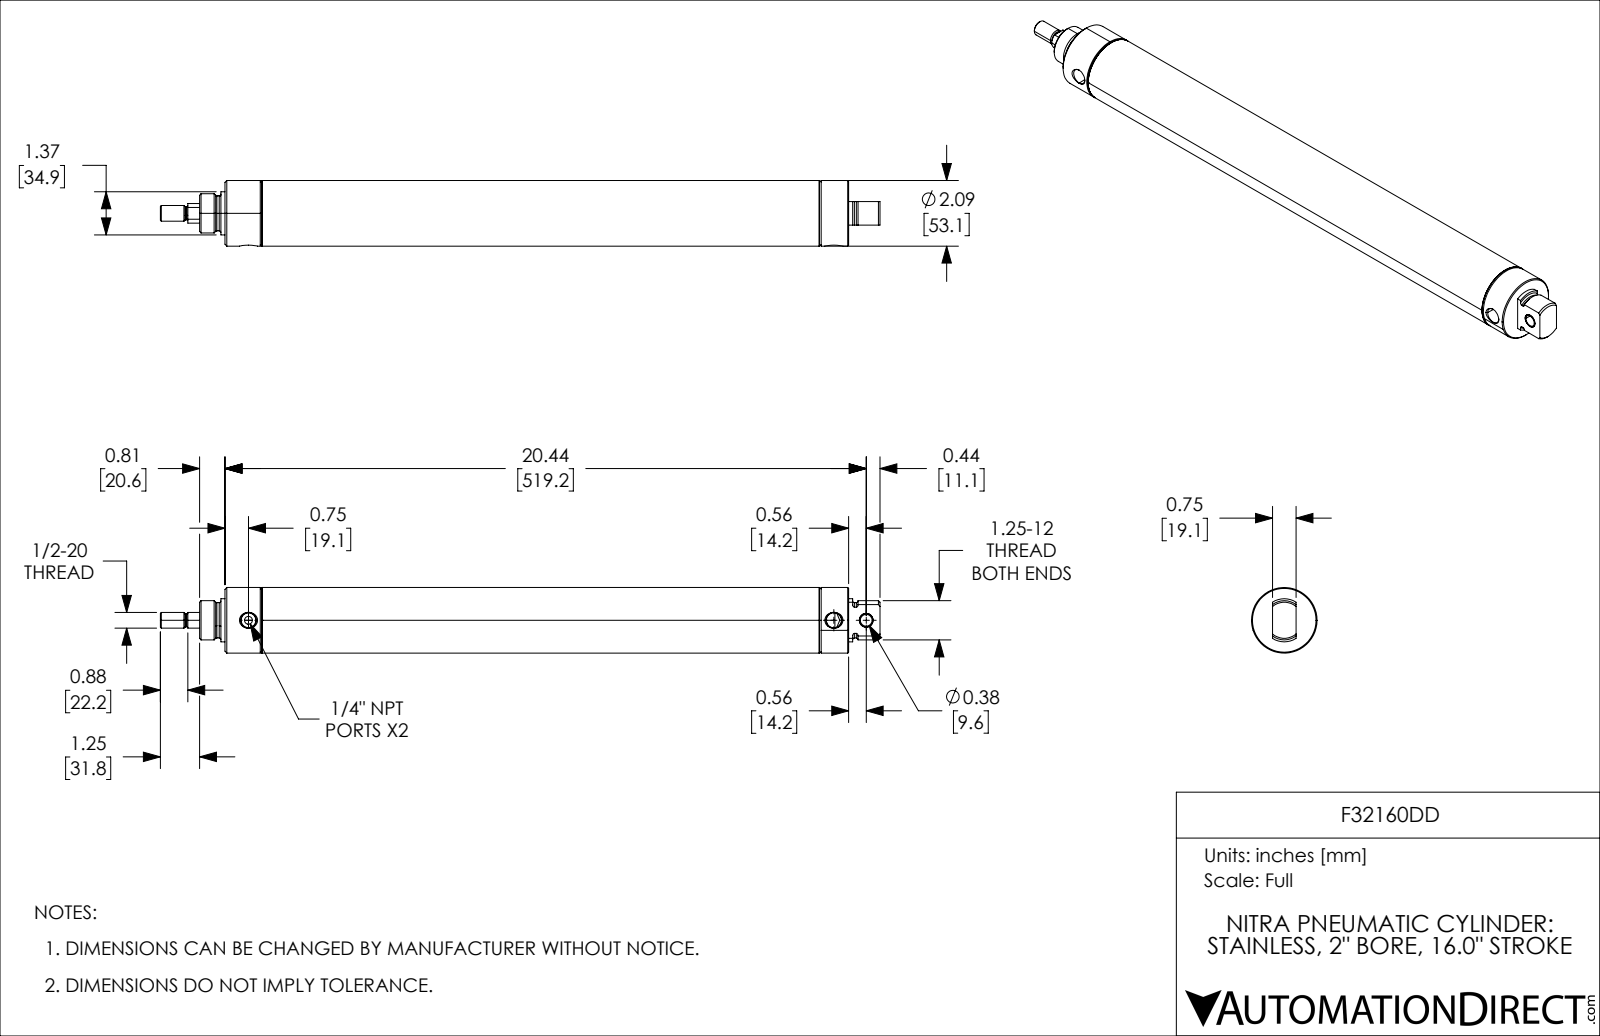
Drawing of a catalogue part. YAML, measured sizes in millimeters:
part_name: "F32160DD_3; F32160DD_9; F32160DD_5; F32160DD_11 (+2 more)"
step_written_by: "SolidWorks 2021 (CONFIG_CONTROL_DESIGN)"
units: millimeters
bodies: {solids: 5, faces: 160, planar: 31, cylindrical: 60, other: 69}
overall_size: [582.62, 53.09, 53.09]
volume: 380430
surface_area: 215410
round_holes:
  - {diameter: 6.35, count: 1}
  - {diameter: 9.55, count: 1}
  - {diameter: 11.15, count: 1}
  - {diameter: 12.18, count: 1}
  - {diameter: 16.52, count: 1}
  - {diameter: 19.05, count: 1}
  - {diameter: 49.05, count: 1}
round_bosses_or_shafts:
  - {diameter: 53.09, count: 1}
  - {diameter: 51.16, count: 1}
  - {diameter: 34.87, count: 1}
  - {diameter: 31.75, count: 1}
  - {diameter: 28.51, count: 1}
  - {diameter: 15.88, count: 1}
  - {diameter: 12.7, count: 1}
  - {diameter: 11.15, count: 1}
partial_cylinders:
  - {radius: 14.25, count: 1}
face_to_face_distances: [30.18, 406.4, 436.58, 466.8, 60.4, 30.22, 436.57, 30.17, 30.23, 38.15]
hole_center_spacings: [26.16, 26.17, 473.96, 500.12, 500.13]
